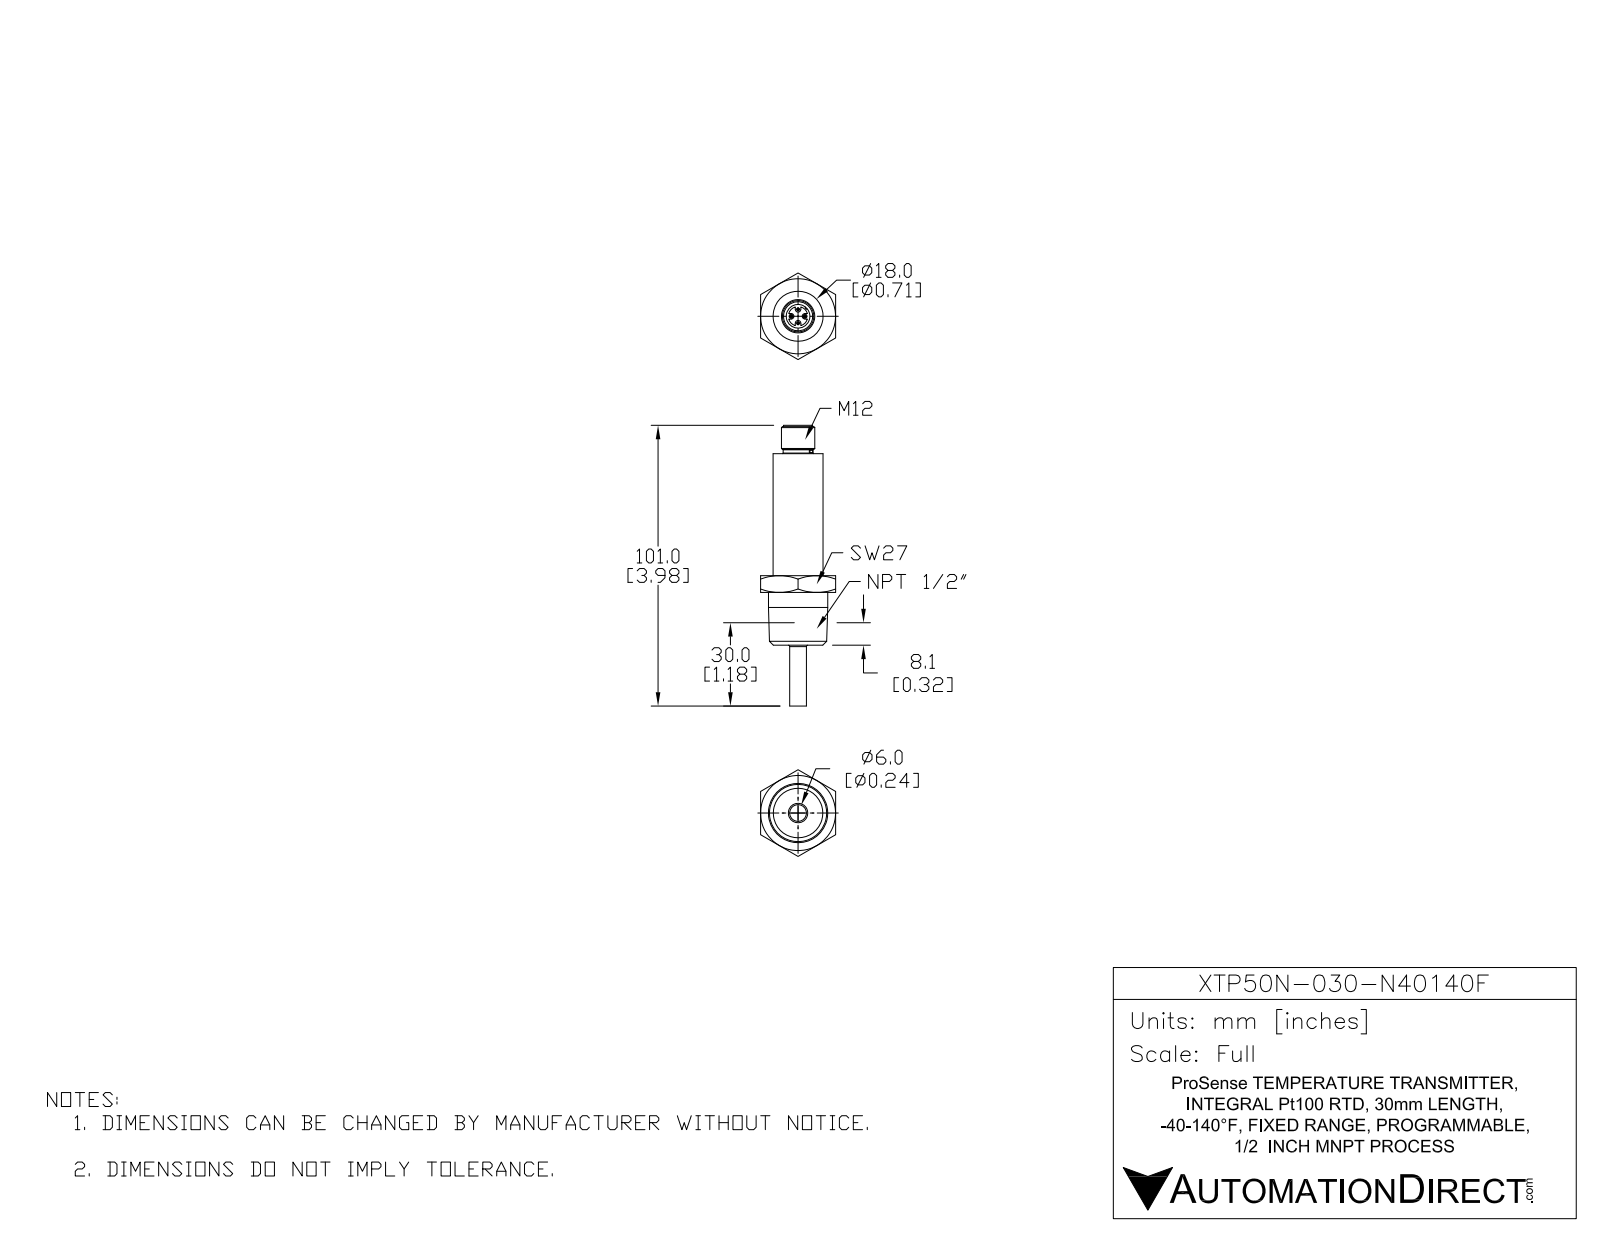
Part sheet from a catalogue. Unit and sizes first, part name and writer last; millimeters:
Units: millimetres
Overall size (bounding box): 101 × 31.18 × 27
Round holes (diameter × count): ⌀4 ×1, ⌀8.5 ×1
Round bosses / shafts (diameter × count): ⌀1.02 ×4, ⌀21.34 ×1, ⌀18 ×1, ⌀12 ×1, ⌀10.7 ×1, ⌀10.5 ×1, ⌀6 ×1
Partial cylindrical surfaces — rounded edges, fillets, slot ends (radius × count): R1 ×4, R3.5 ×1, R4.25 ×1
Main face-to-face distances: 27, 25, 19, 6, 68.9, 49.9, 43.9, 79.1, 60.1, 54.1
Volume: 22 355 mm³ · Surface area: 6 897 mm²
Bodies: 1 solid, 117 faces (43 planar, 34 cylindrical, 40 other)
Part name (STEP PRODUCT): XTP50N-030-N40140F
STEP written by: SolidWorks 2015 (AUTOMOTIVE_DESIGN)
